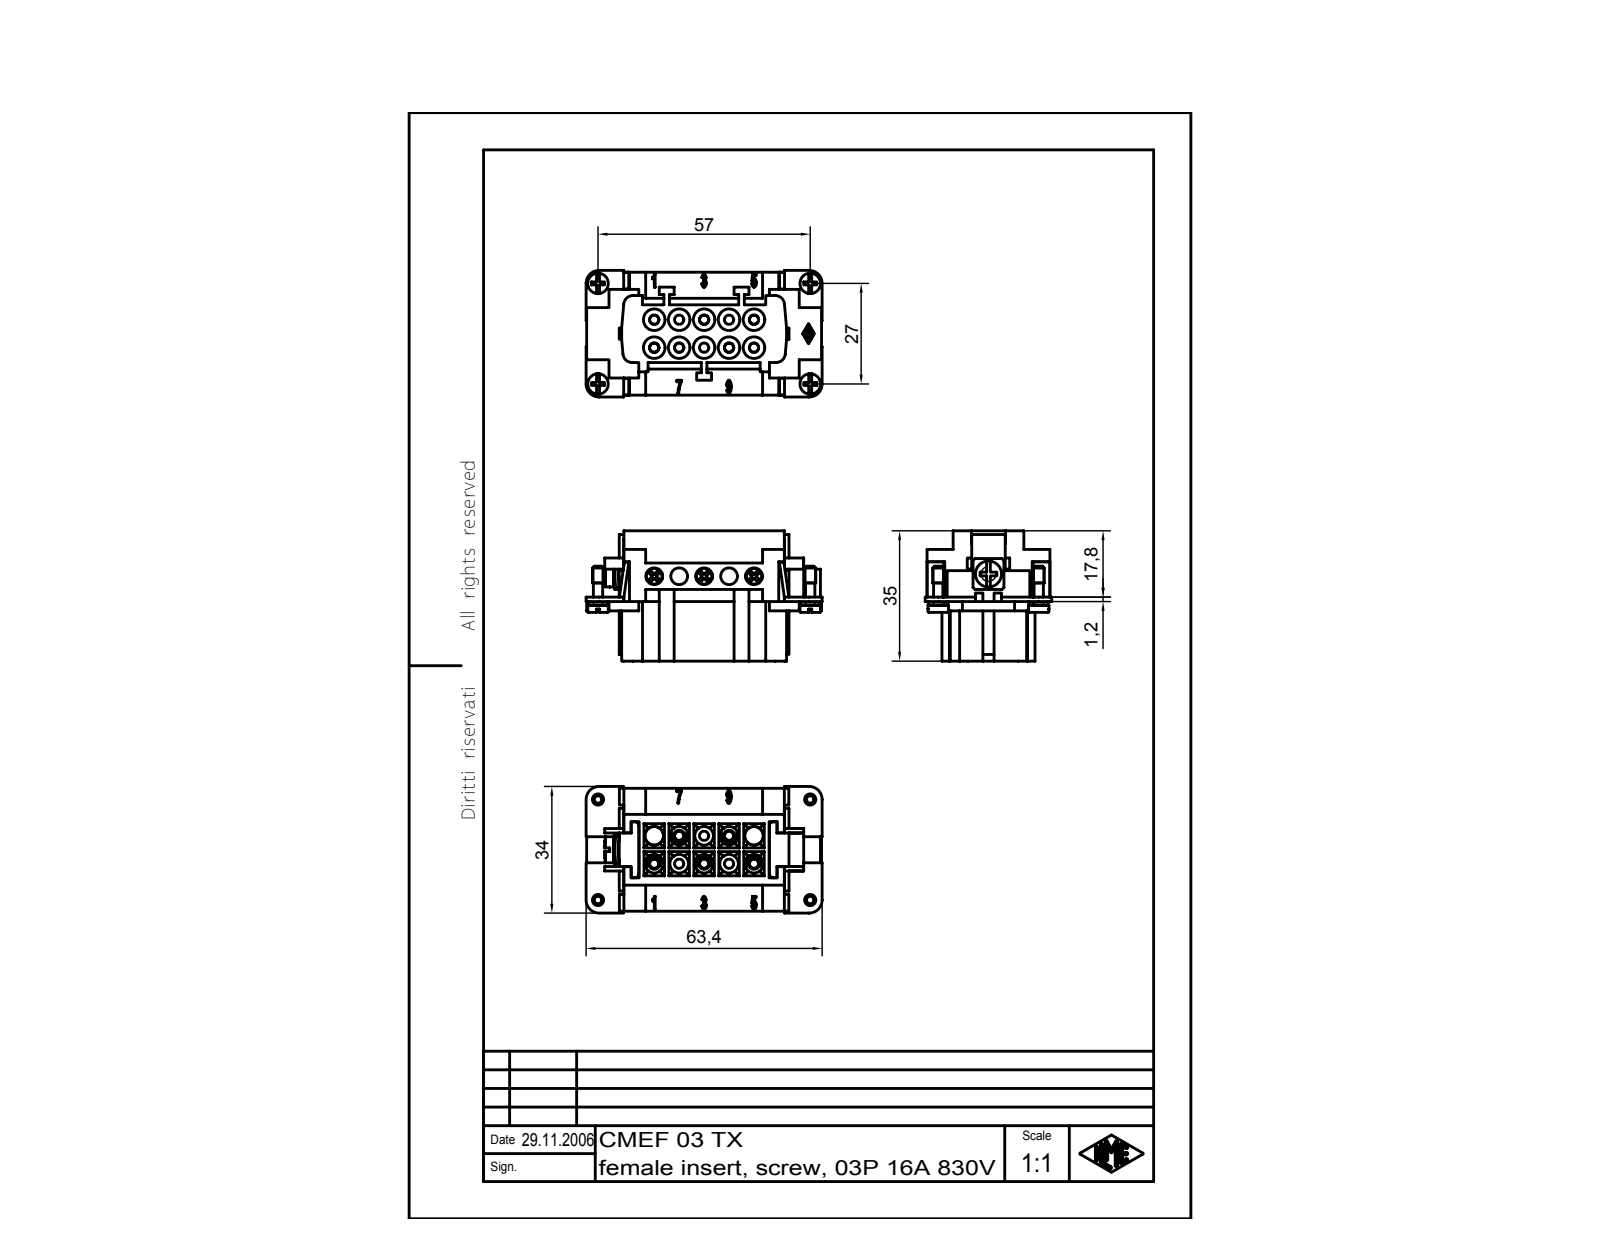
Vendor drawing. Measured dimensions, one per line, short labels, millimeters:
name: CMEF 03 TX
written by: Autodesk Inventor 7 (AUTOMOTIVE_DESIGN)
unit: mm
bodies: 14 solids, 1013 faces (495 planar, 147 cylindrical, 371 other)
size: 63.4 × 35 × 34
volume: 29 623 mm³; area: 22 541 mm²
holes: 5× ⌀3, 5× ⌀4.5, 5× ⌀5, 2× ⌀2.55
bosses: 8× ⌀2.5, 5× ⌀4.2, 2× ⌀5.5, 2× ⌀5.3, 2× ⌀3, 1× ⌀7
rounds: 14× R0.1, 5× R2.1, 4× R2.5, 2× R1, 2× R3.5, 1× R1.62, 1× R5.5
face distances: 1.75, 16, 17.25, 19, 7, 8.75, 26, 24.25, 15.5, 3.25
hole spacings: 6.7, 13.4, 10.06, 15.36, 20.1, 7.5, 26.8, 17.97
